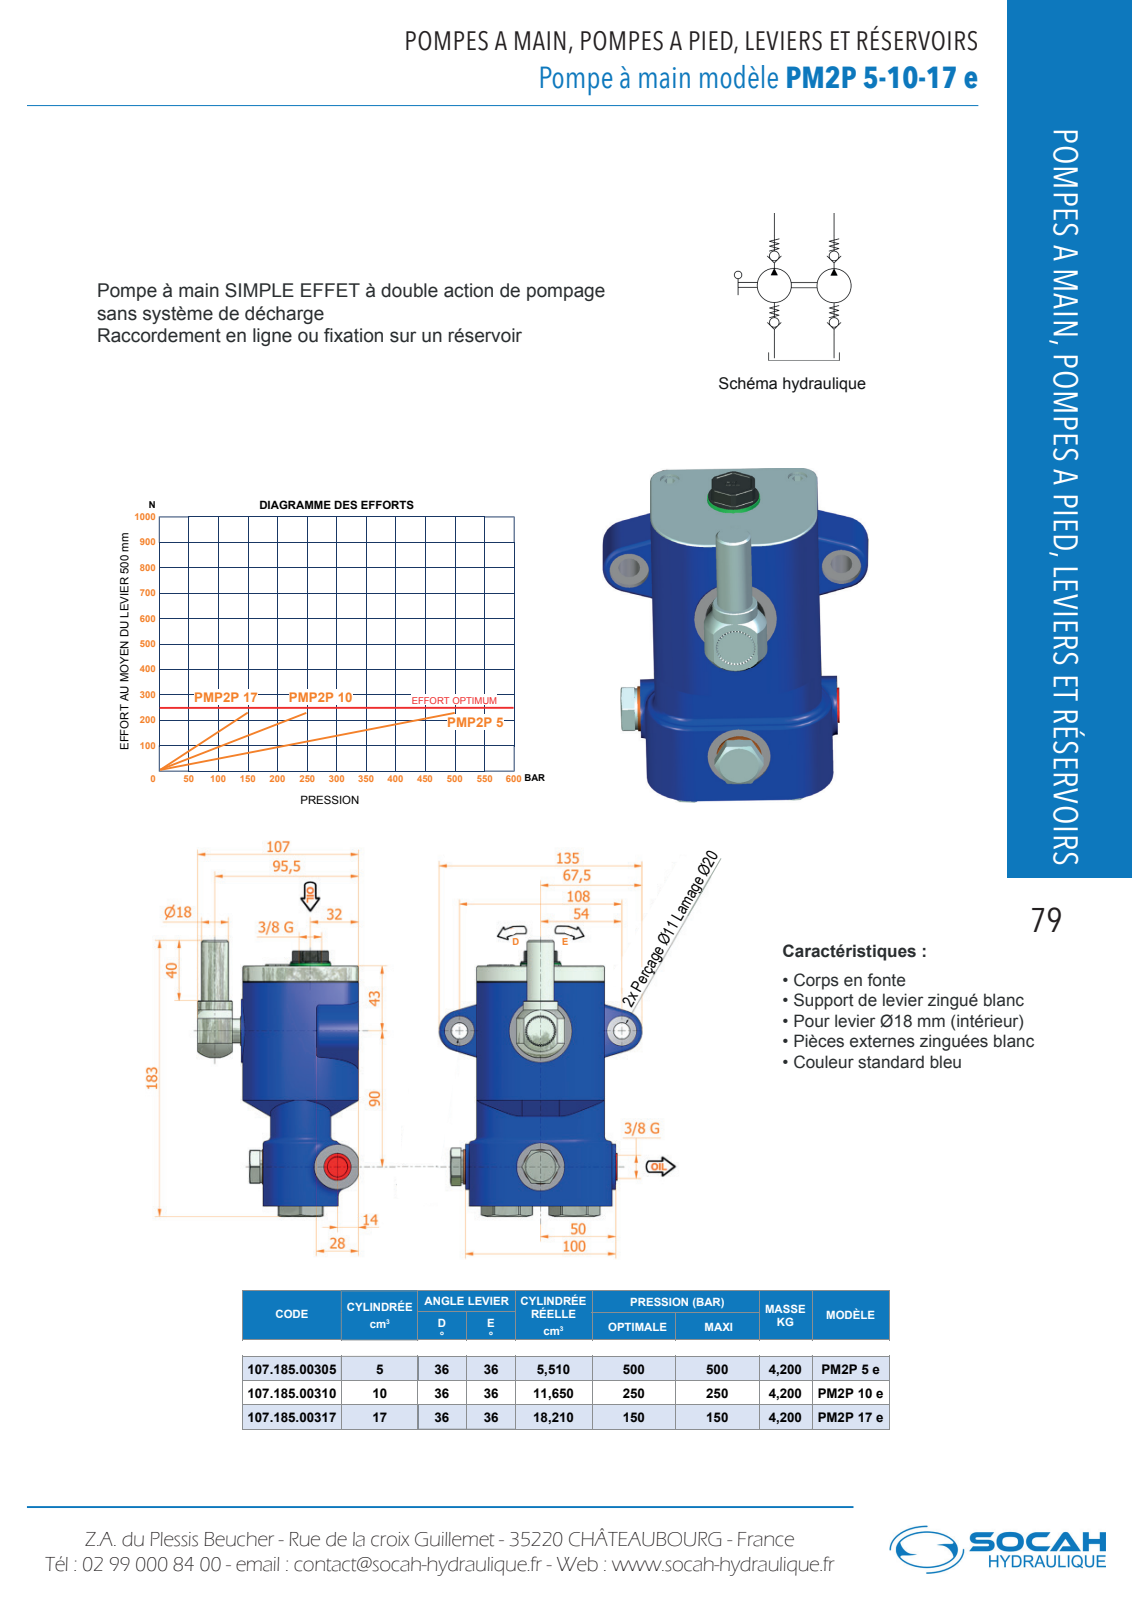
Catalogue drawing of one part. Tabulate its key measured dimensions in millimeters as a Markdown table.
| quantity | value |
| --- | --- |
| part name | 6092.0001.00.50 Bloccato |
| STEP written by | Autodesk Inventor 2010 (AUTOMOTIVE_DESIGN) |
| units | millimeters |
| bodies | 0 solids, 1826 faces (560 planar, 635 cylindrical, 631 other) |
| overall size | 183.1 × 135 × 107 |
| round holes (diameter × count) | 10 × 2, 20 × 2, 25 × 2, 28.5 × 2, 4.92 × 1, 17 × 1, 27 × 1 |
| round bosses / shafts (diameter × count) | 23 × 3, 24 × 2, 21 × 2, 18 × 2, 14 × 2, 6 × 2, 42 × 1, 27 × 1 |
| partial cylindrical surfaces (radius × count) | 5.46 × 76, 5.48 × 76, 0.5 × 24, 2 × 17, 0.15 × 12, 0.2 × 12, 1 × 7, 0.36 × 6 |
| main face-to-face distances | 6, 5, 85, 79, 71, 80, 159.1, 154.1, 74.1, 73 |
| hole center spacings | 61.28, 45, 90.1 |
